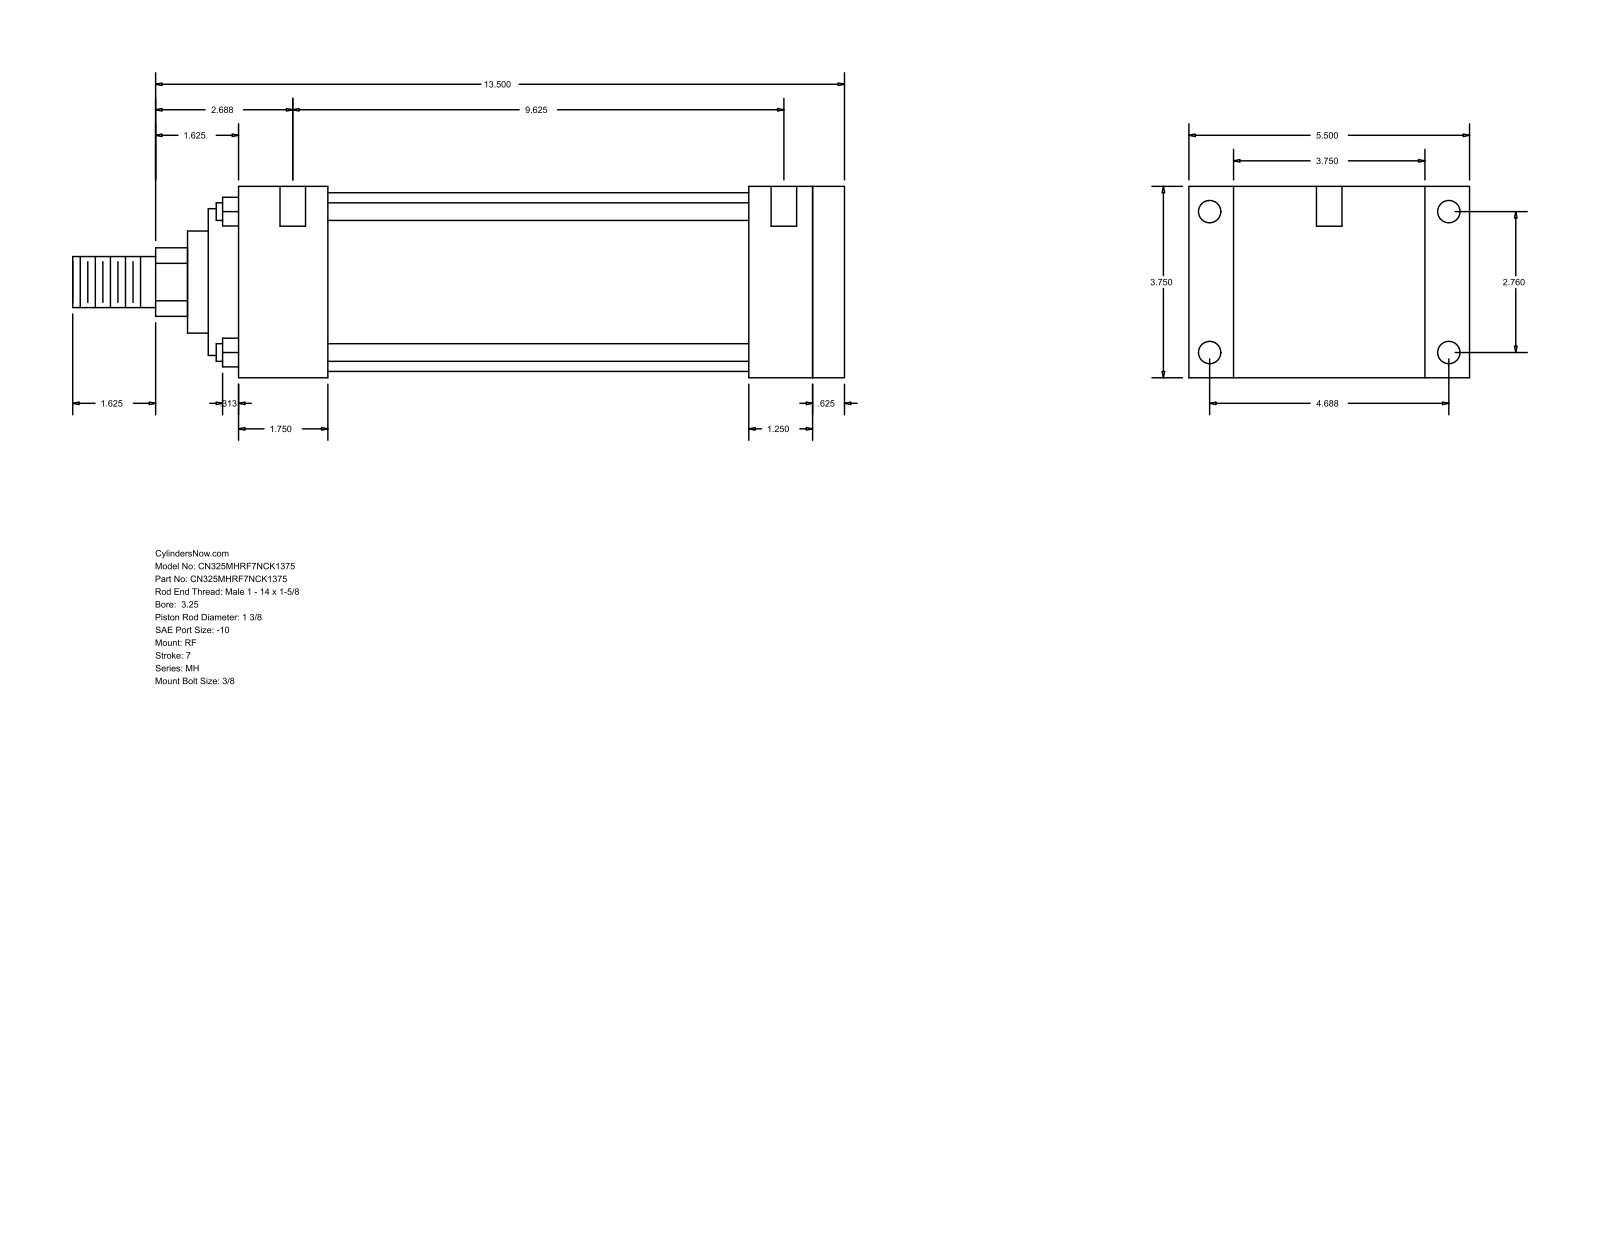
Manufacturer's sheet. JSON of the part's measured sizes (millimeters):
{"part_name": "MH_RF__0325_1.375", "step_written_by": "GSSL Pune (CONFIG_CONTROL_DESIGN)", "units": "millimeters", "bodies": {"solids": 0, "faces": 94, "planar": 65, "cylindrical": 29, "other": 0}, "overall_size": [384.18, 139.7, 95.25], "round_holes": [[5.56, 4], [11.13, 4], [12.7, 2]], "round_bosses_or_shafts": [[8.76, 4], [88.9, 1], [73.03, 1], [50.8, 1], [34.92, 1], [25.4, 1]], "partial_cylinders_radius": [[17.06, 1]], "face_to_face_distances": [95.24, 301.63, 15.88, 285.75, 22.23, 117.47, 44.45, 241.3, 257.18, 254], "hole_center_spacings": [70.1, 119.06, 138.16, 250.83, 1.59, 4.76, 244.48, 246.07]}
